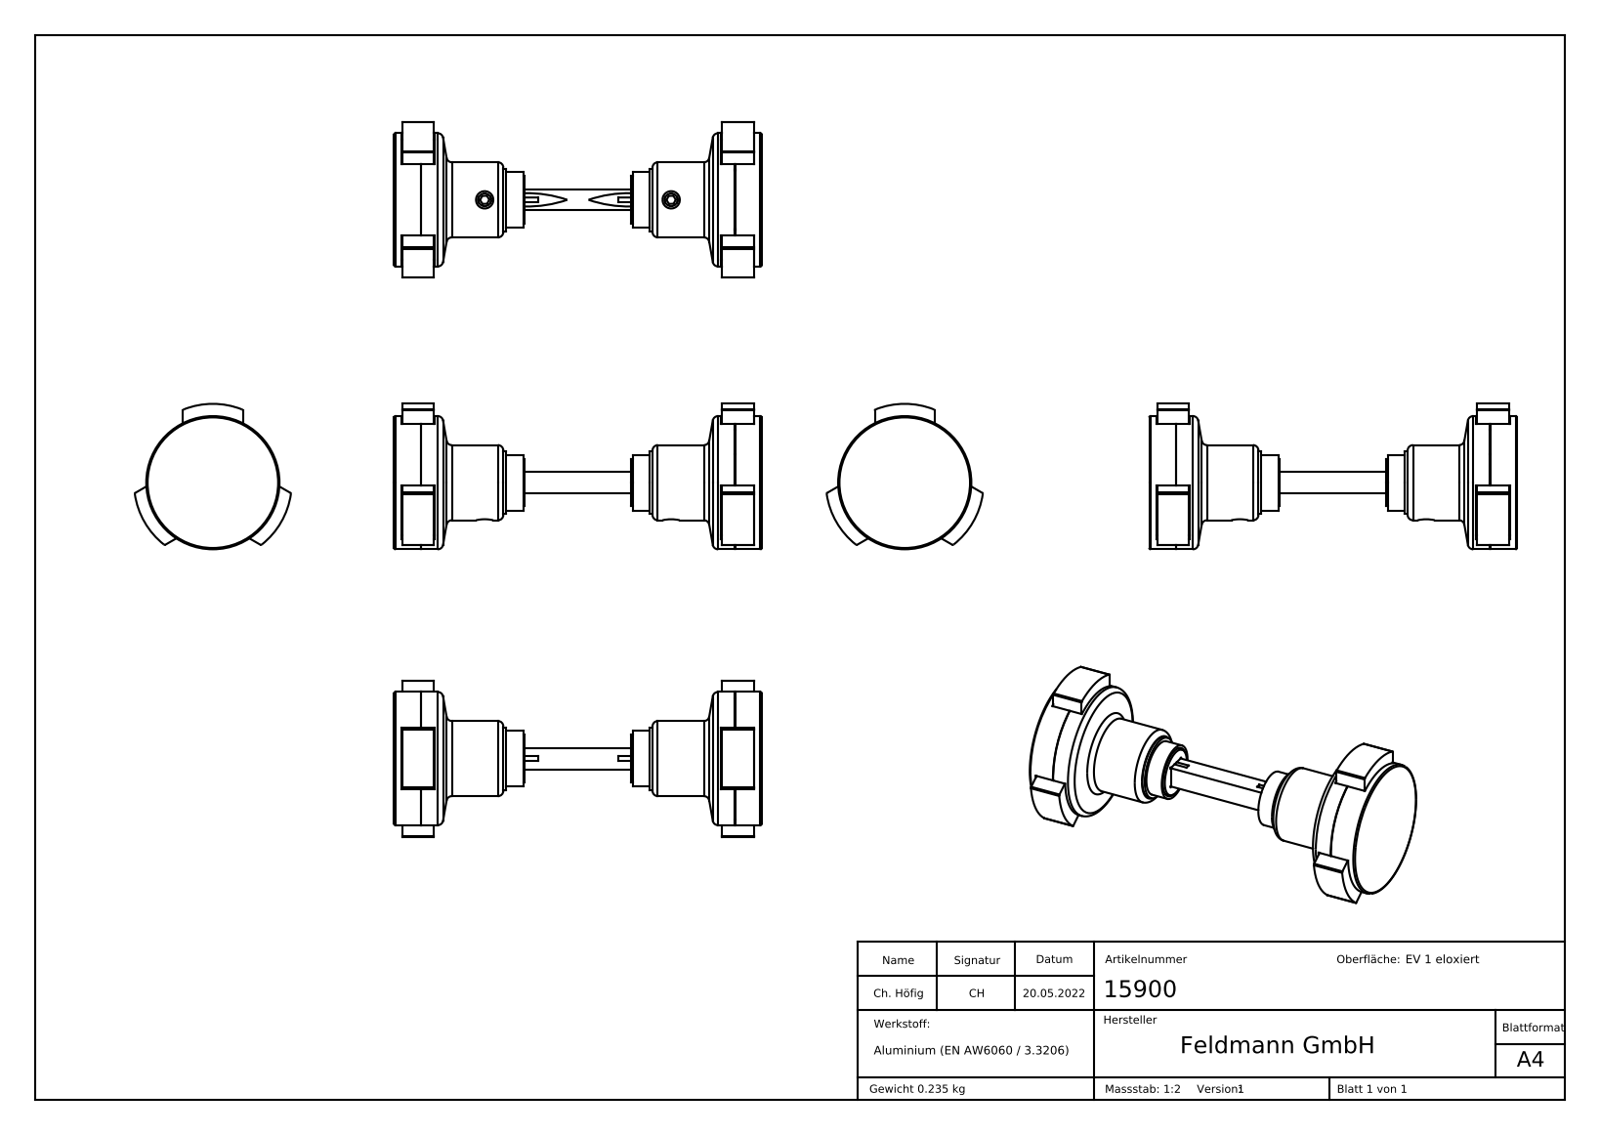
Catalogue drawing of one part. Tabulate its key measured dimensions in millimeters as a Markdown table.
| quantity | value |
| --- | --- |
| part name | DIN914_DIN 914 M6x8; 15900 Teil3_15900 Teil3; 15900 Teil2_15900 Teil2; 15900 Teil1_15900 Teil1 (+1 more) |
| STEP written by | SolidWorks 2018 (CONFIG_CONTROL_DESIGN) |
| units | millimeters |
| bodies | 15 solids, 640 faces (360 planar, 50 cylindrical, 230 other) |
| overall size | 138 × 58.59 × 54.6 |
| volume | 111 669 mm³ |
| surface area | 49 393 mm² |
| round holes (diameter × count) | 5 × 2, 6.5 × 2, 18.8 × 1, 21.6 × 1 |
| round bosses / shafts (diameter × count) | 6 × 2, 50 × 1, 28.2 × 1, 23.5 × 1, 21.4 × 1, 20.8 × 1, 17.7 × 1 |
| partial cylindrical surfaces (radius × count) | 0.5 × 6, 0.25 × 4, 29.6 × 1 |
| main face-to-face distances | 10, 128, 10.1, 127.9, 117.9, 8.1, 138, 120.1, 7.15, 8 |
| hole center spacings | 70 |
